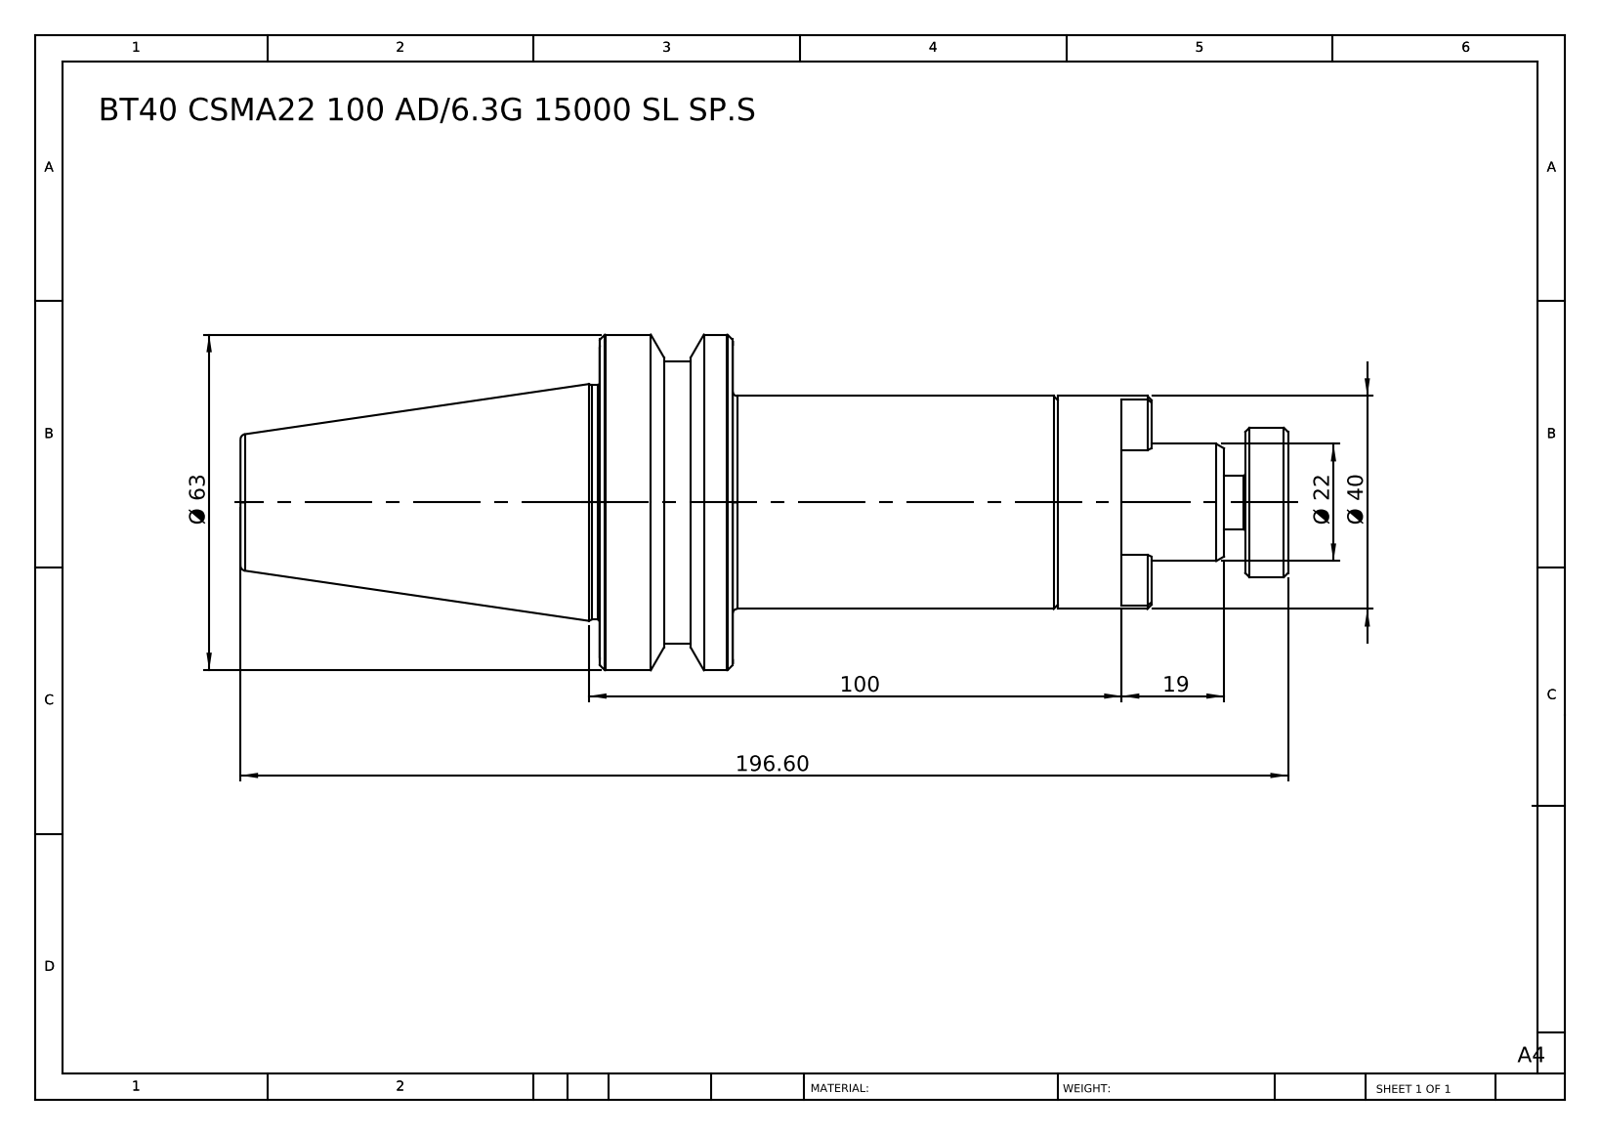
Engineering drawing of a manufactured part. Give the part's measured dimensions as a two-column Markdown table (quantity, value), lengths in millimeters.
| quantity | value |
| --- | --- |
| part name | BT40 CSMA22 100 AD-6.3G15000 SL SP |
| STEP written by | SolidWorks 2014 (CONFIG_CONTROL_DESIGN) |
| units | millimeters |
| bodies | 2 solids, 86 faces (22 planar, 20 cylindrical, 44 other) |
| overall size | 196.6 × 63 × 63 |
| volume | 243 708 mm³ |
| surface area | 34 324 mm² |
| round holes (diameter × count) | 22 × 1 |
| round bosses / shafts (diameter × count) | 63 × 1, 53 × 1, 44 × 1, 40 × 1, 28 × 1, 10 × 1 |
| main face-to-face distances | 25, 12, 61, 86, 31.2, 61.2, 86.2, 11.8, 73, 98 |
